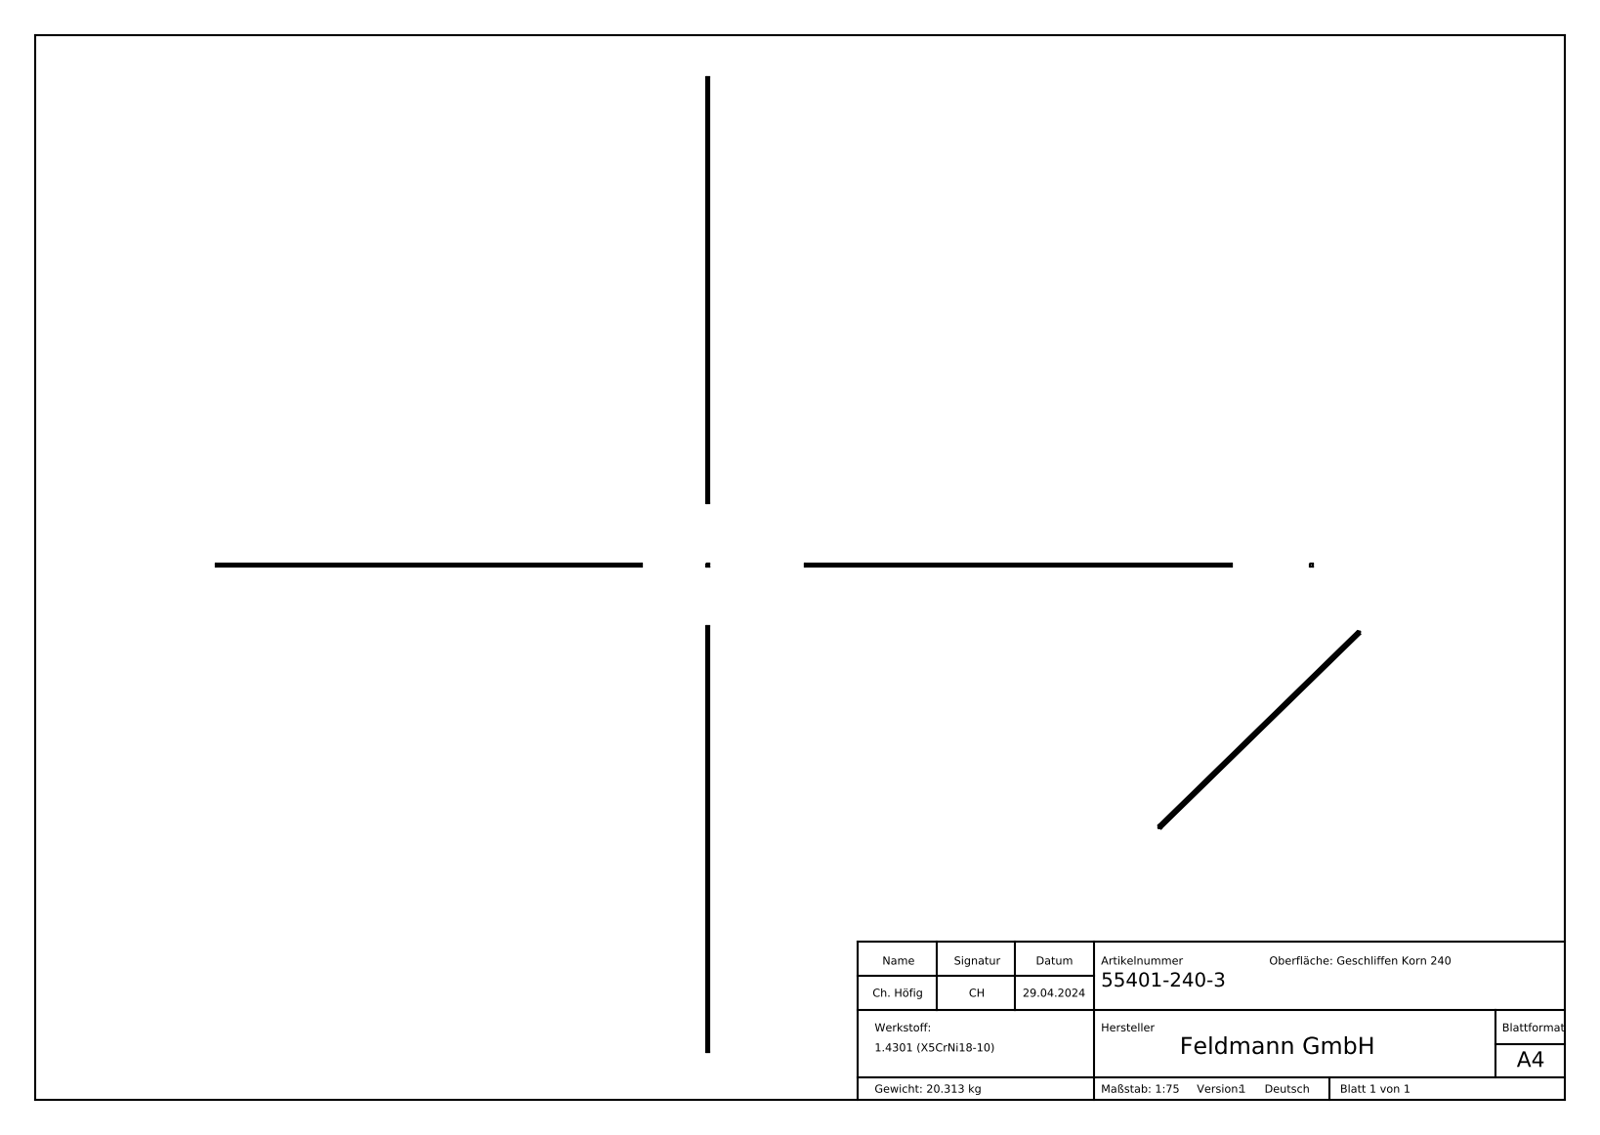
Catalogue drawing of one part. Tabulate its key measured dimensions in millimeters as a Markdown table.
| quantity | value |
| --- | --- |
| part name | 55401-240-3 |
| STEP written by | SolidWorks 2018 (CONFIG_CONTROL_DESIGN) |
| units | millimeters |
| bodies | 1 solid, 304 faces (174 planar, 8 cylindrical, 122 other) |
| overall size | 6000 × 40 × 40 |
| volume | 2 571 000 mm³ |
| surface area | 1 715 000 mm² |
| partial cylindrical surfaces (radius × count) | 1.5 × 4, 4.5 × 4 |
| main face-to-face distances | 3, 37, 40, 34, 6000, 2.9, 34.1, 37.1, 1.82, 3.21 |
